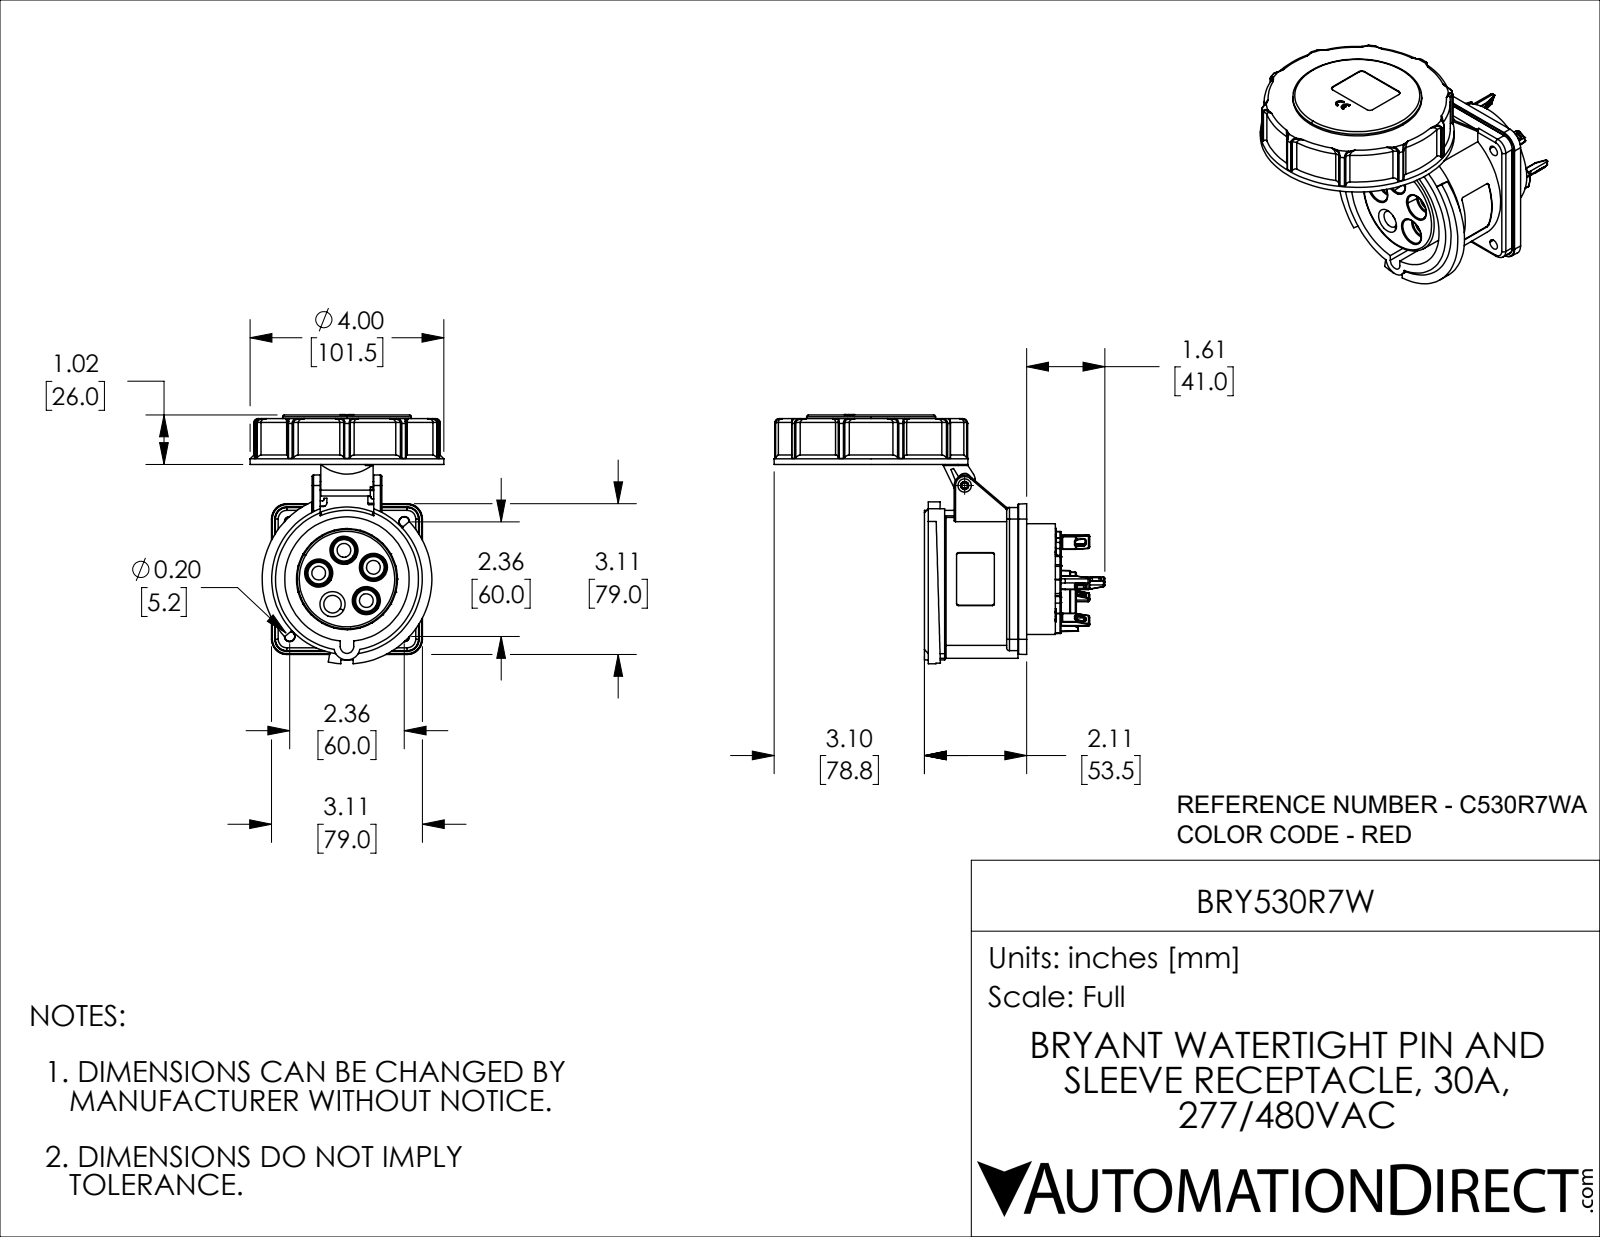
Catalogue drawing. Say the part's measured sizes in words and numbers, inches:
The part is named "BRY530R7W". Its 3-D file was written by "SolidWorks 2021 (CONFIG_CONTROL_DESIGN)". It is 2 solids with 1894 faces: 660 planar, 535 cylindrical and 699 other. Overall it measures 6.821 by 5.139 by 3.996 inches. Its volume is 24.53 cubic inches and its surface area 137.2 square inches. Round holes: 4 of diameter 0.217, 4 of diameter 0.283, 1 of diameter 0.118, 1 of diameter 0.165, 1 of diameter 0.276, 1 of diameter 0.362, 1 of diameter 2.559, 1 of diameter 2.567, 1 of diameter 3.602. Round bosses or shafts: 1 of diameter 3.996, 1 of diameter 3.106, 1 of diameter 2.772, 1 of diameter 2.657, 1 of diameter 2.283, 1 of diameter 0.157. Partial cylindrical surfaces (rounded edges, fillets, slot ends): 96 of radius 0.01, 64 of radius 0.02, 30 of radius 0.031, 24 of radius 0.098, 19 of radius 0.039, 8 of radius 0.01, 8 of radius 0.03, 8 of radius 0.077. The main face-to-face distances are 0.079, 0.827, 0.118, 0.906, 2.028, 0.413, 1.024, 0.945, 1.693, 0.807. The hole center spacings are 0.596, 1.135, 1.67, 2.362, 0.701, 0.702, 3.341, 1.075.
